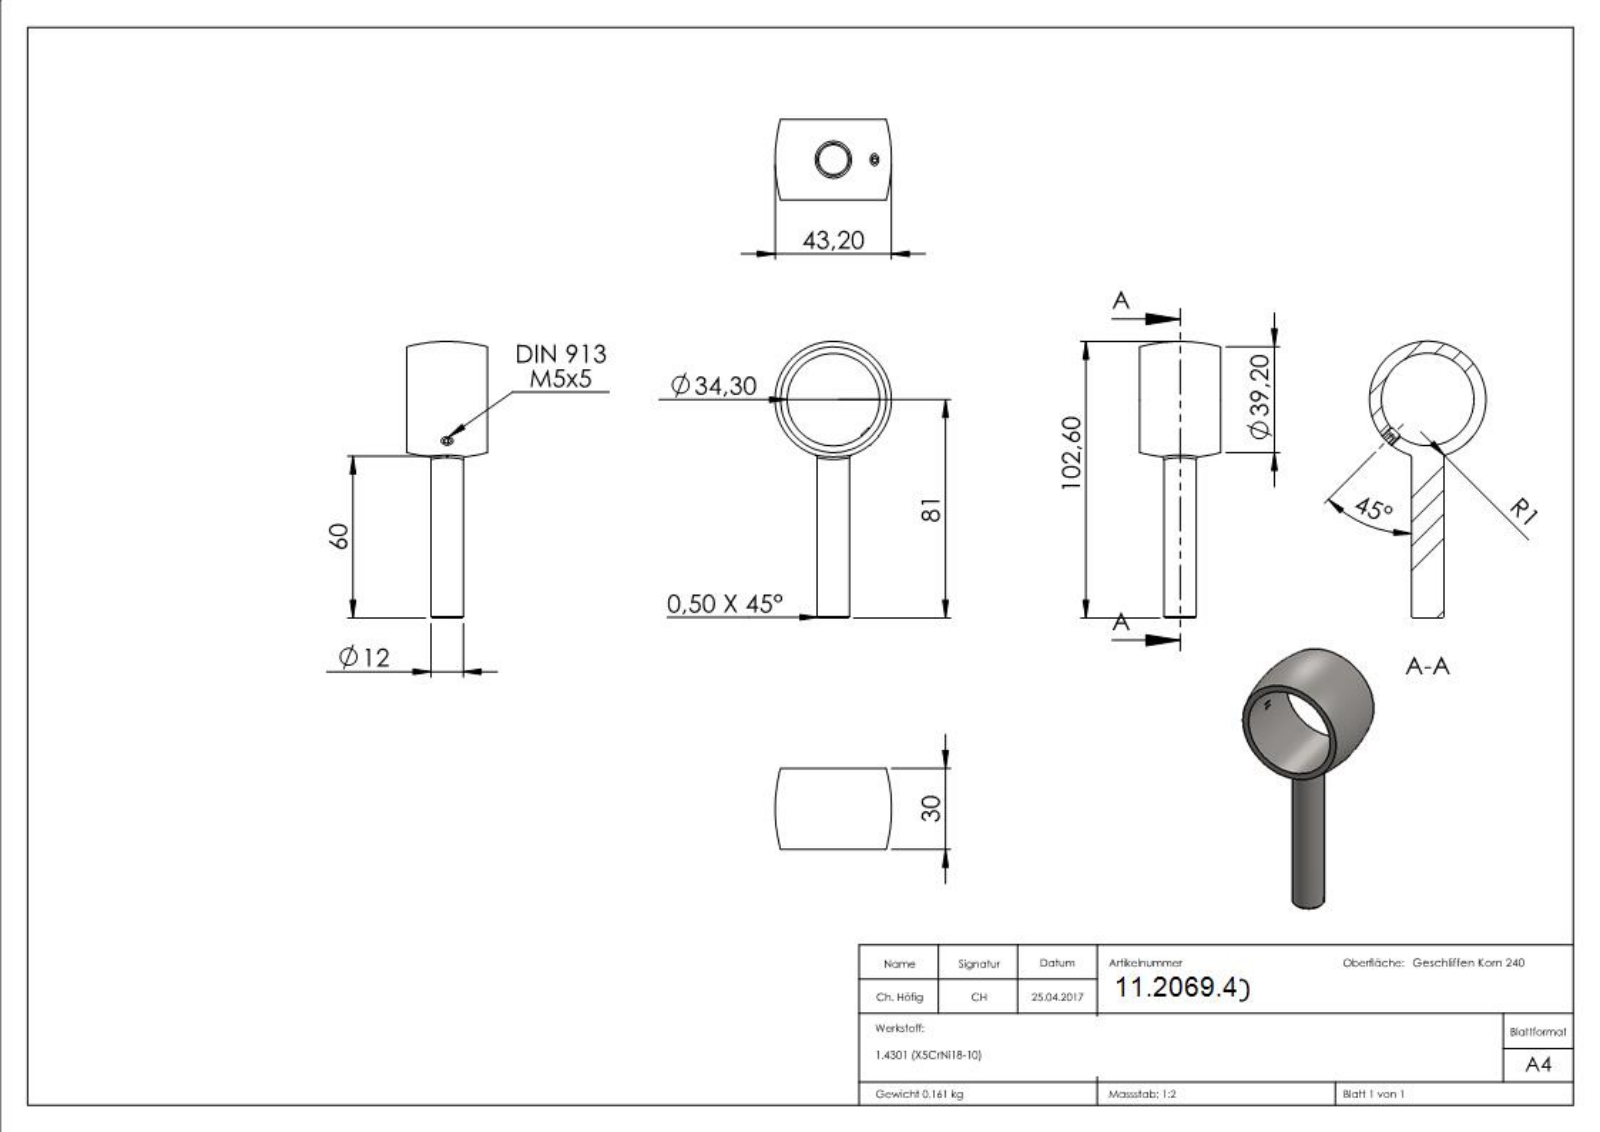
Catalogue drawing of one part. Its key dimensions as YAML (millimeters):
part_name: "50391-240 Teil1; DIN913 M5x5; DIN913 M5x5_M5x5 Keyshot; 50391-240 (+2 more)"
step_written_by: "SolidWorks 2018 (CONFIG_CONTROL_DESIGN)"
units: millimeters
bodies: {solids: 3, faces: 73, planar: 21, cylindrical: 23, other: 29}
overall_size: [102.6, 82.91, 30]
volume: 20465
surface_area: 10363
round_holes:
  - {diameter: 4.2, count: 1}
  - {diameter: 34.3, count: 1}
round_bosses_or_shafts:
  - {diameter: 12, count: 1}
  - {diameter: 5, count: 1}
partial_cylinders:
  - {radius: 0.2, count: 18}
face_to_face_distances: [30, 2.5, 5, 13.75, 16.25]
